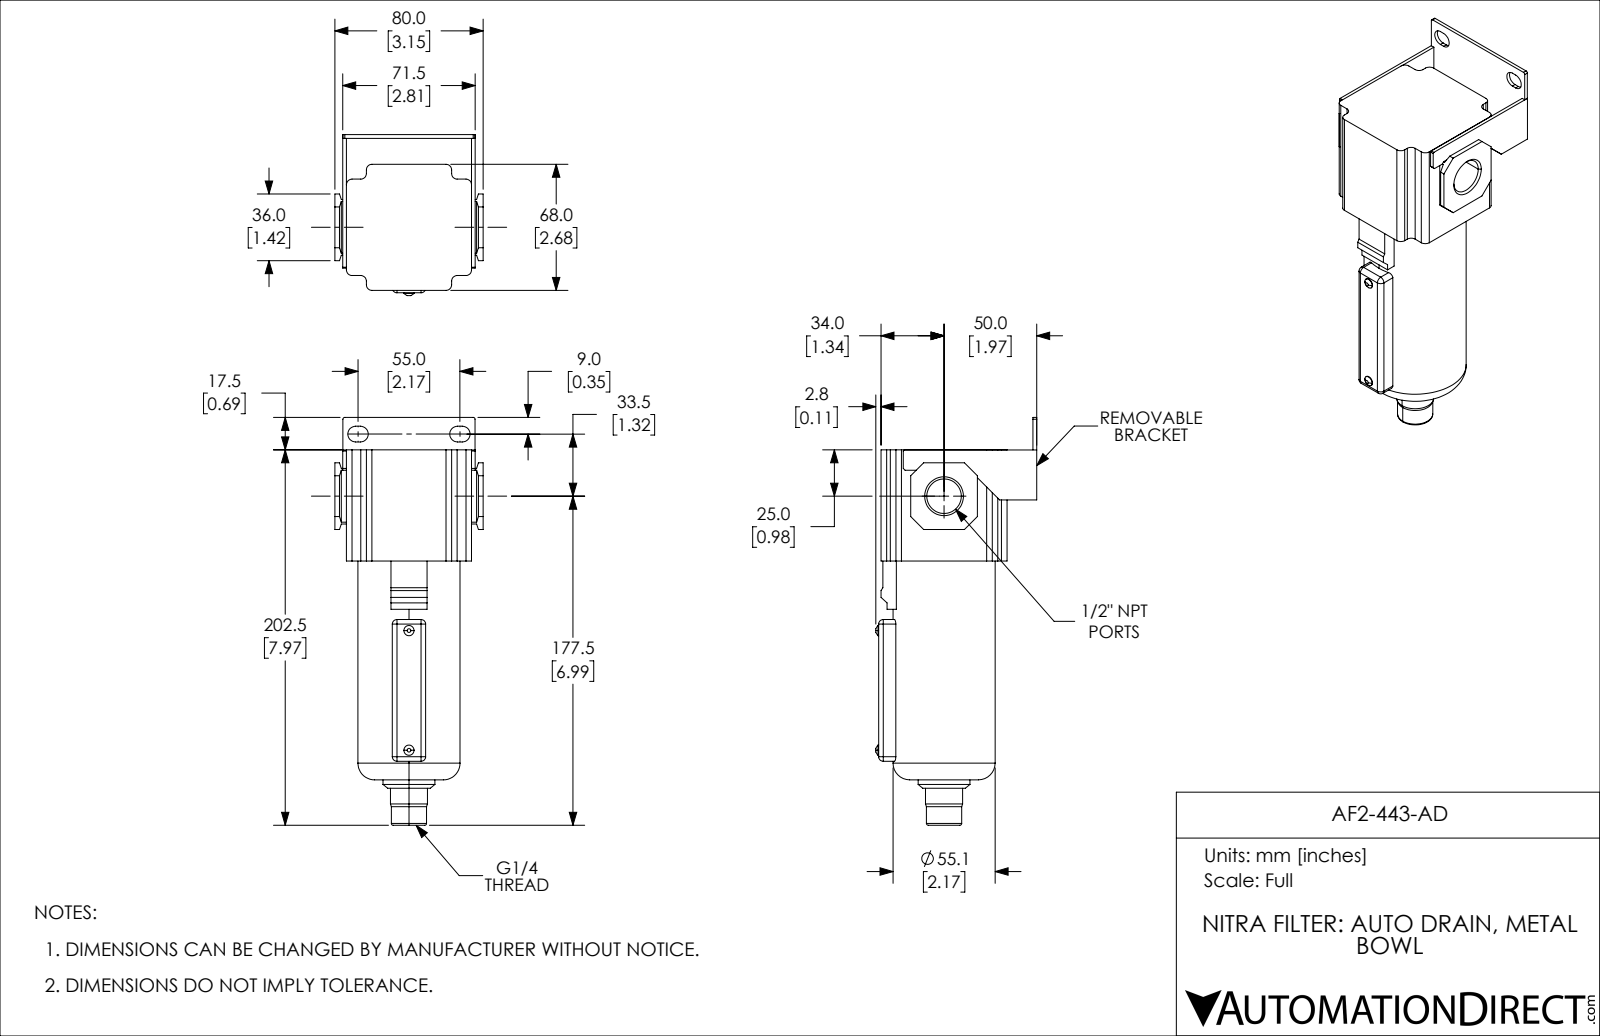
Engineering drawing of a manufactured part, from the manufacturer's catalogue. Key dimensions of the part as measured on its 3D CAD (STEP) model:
Part name (STEP PRODUCT): AF2-443-AD
STEP written by: SolidWorks 2019 (CONFIG_CONTROL_DESIGN)
Units: millimetres
Bodies: 1 solid, 161 faces (95 planar, 44 cylindrical, 22 other)
Overall size (bounding box): 220 × 86.8 × 80
Volume: 567 219 mm³ · Surface area: 61 405 mm²
Round holes (diameter × count): ⌀8.57 ×1, ⌀18.63 ×1
Round bosses / shafts (diameter × count): ⌀5.5 ×2, ⌀55.1 ×1, ⌀28 ×1, ⌀20 ×1, ⌀19 ×1
Partial cylindrical surfaces — rounded edges, fillets, slot ends (radius × count): R3 ×12, R2.5 ×8, R4.25 ×4, R1 ×2
Main face-to-face distances: 2, 14, 60, 16, 82, 68, 84, 69.5, 67.5, 4.25
